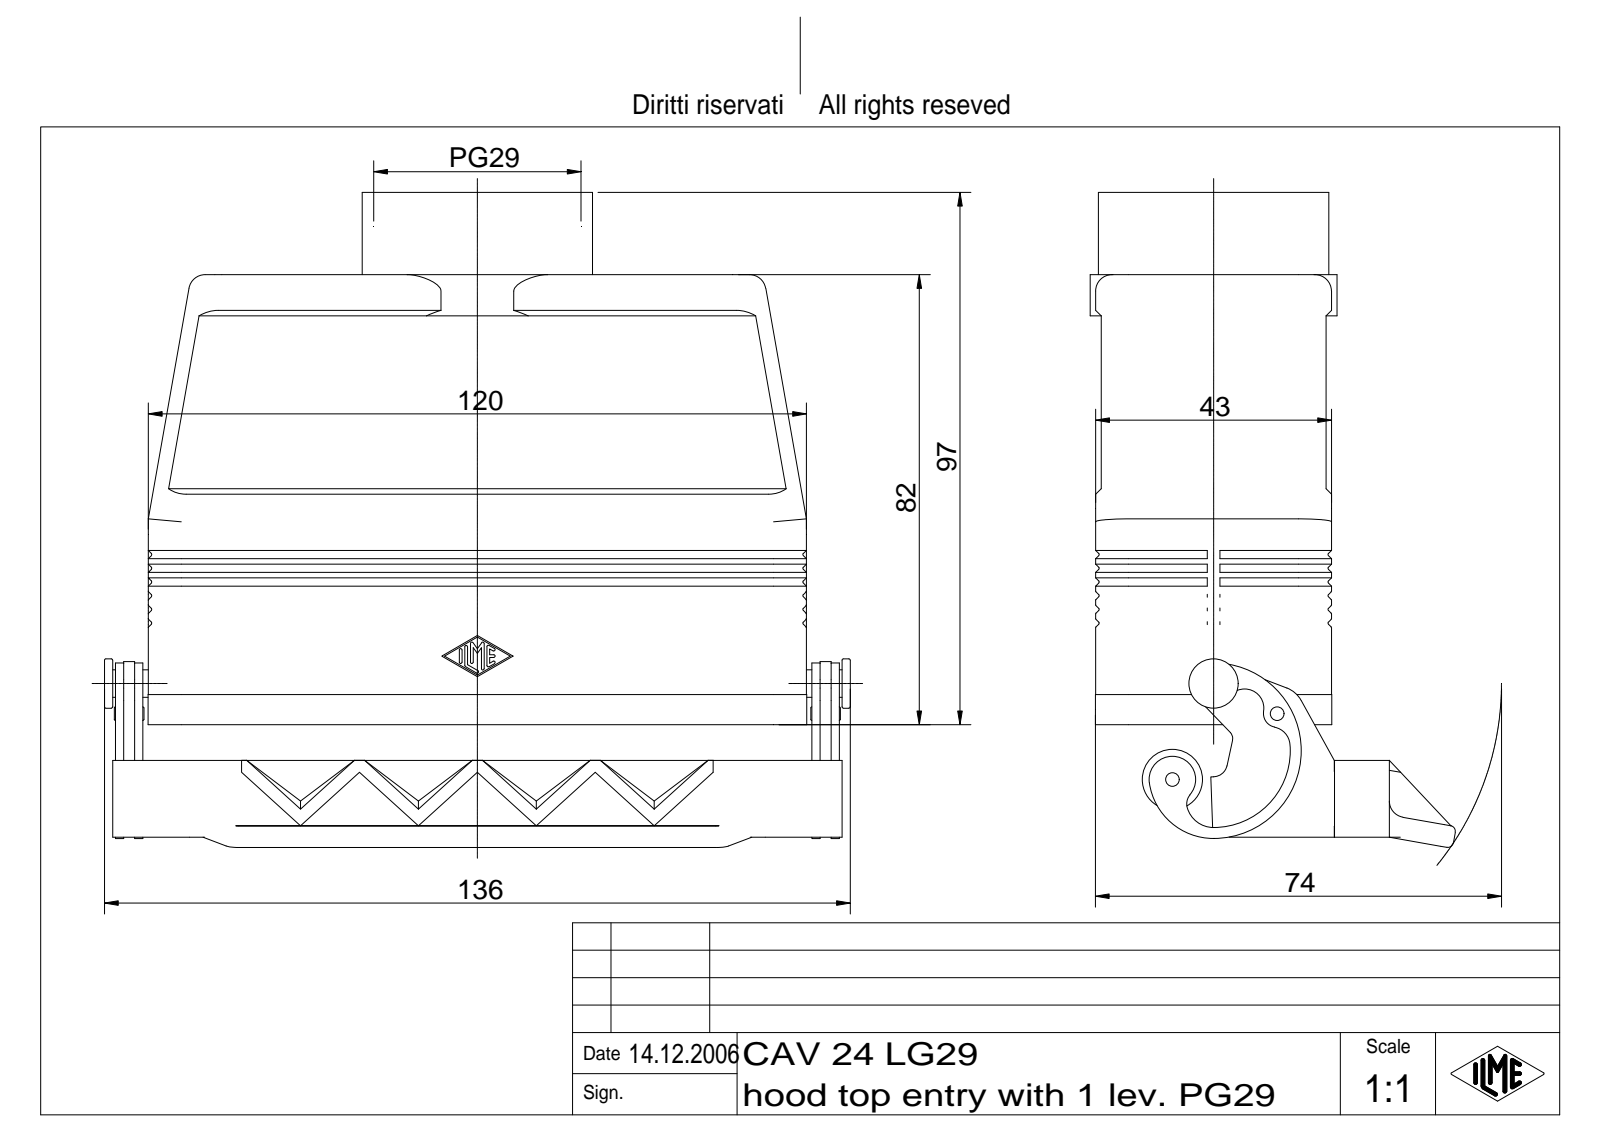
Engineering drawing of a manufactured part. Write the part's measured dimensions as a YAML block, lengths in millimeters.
part_name: "CAV 24 LG29"
step_written_by: "Autodesk Inventor 7 (AUTOMOTIVE_DESIGN)"
units: millimeters
bodies: {solids: 1, faces: 960, planar: 235, cylindrical: 324, other: 401}
overall_size: [136, 119.37, 66.59]
volume: 126203
surface_area: 74939
round_holes:
  - {diameter: 2.5, count: 1}
  - {diameter: 33.48, count: 1}
  - {diameter: 35.48, count: 1}
round_bosses_or_shafts:
  - {diameter: 45, count: 1}
  - {diameter: 42, count: 1}
  - {diameter: 11, count: 1}
  - {diameter: 9, count: 1}
  - {diameter: 5, count: 1}
  - {diameter: 3.1, count: 1}
  - {diameter: 2, count: 1}
partial_cylinders:
  - {radius: 0.2, count: 52}
  - {radius: 0.25, count: 32}
  - {radius: 2.5, count: 9}
  - {radius: 6, count: 8}
  - {radius: 3, count: 7}
  - {radius: 1, count: 6}
  - {radius: 2.45, count: 4}
  - {radius: 6.05, count: 4}
face_to_face_distances: [3.45, 3.5, 39.55, 39.5, 36.05, 36, 36.1, 2.5, 2.45, 1]
